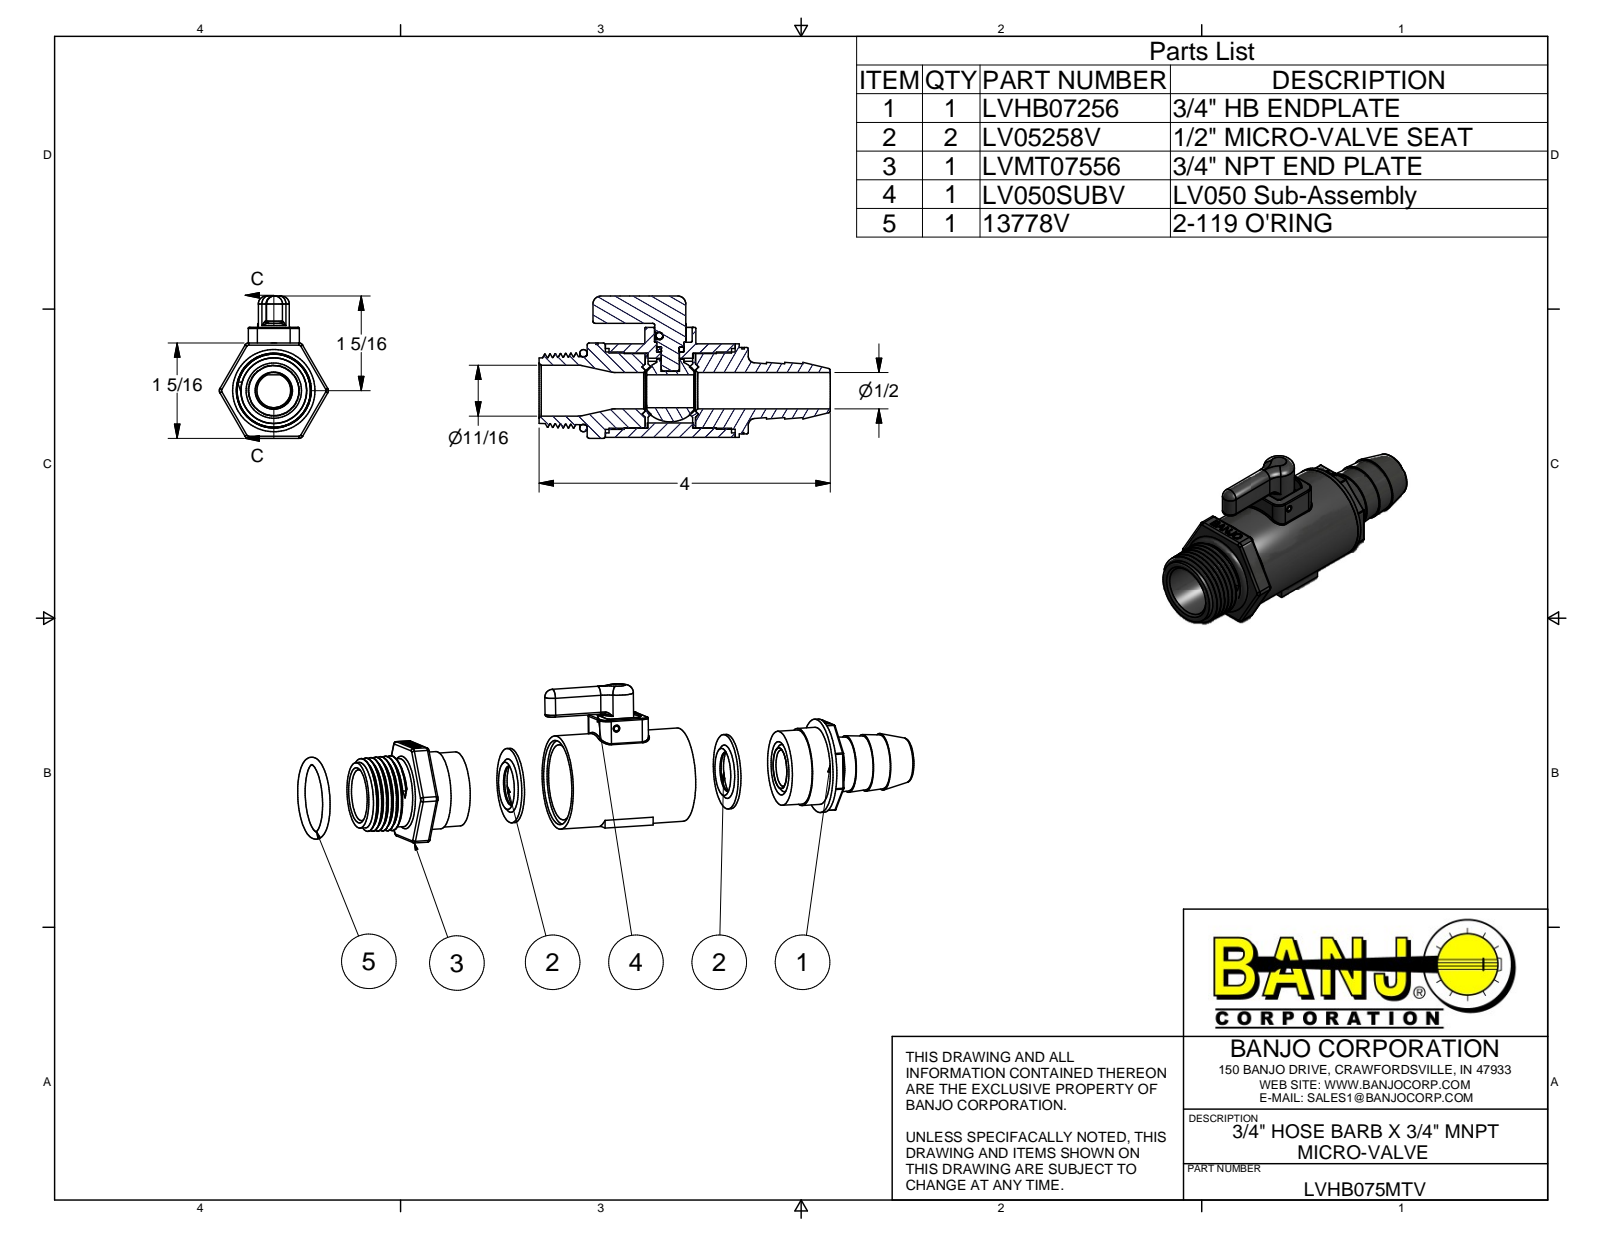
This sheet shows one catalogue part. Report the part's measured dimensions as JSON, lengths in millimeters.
{"part_name": "LV05254A; LV02153B; AQ010V; WS10002 (+7 more)", "step_written_by": "Autodesk Inventor 2014 (AUTOMOTIVE_DESIGN)", "units": "millimeters", "bodies": {"solids": 10, "faces": 701, "planar": 290, "cylindrical": 133, "other": 278}, "overall_size": [101.52, 49.71, 38.02], "volume_mm3": 51198, "surface_area_mm2": 30132, "round_holes": [[2.36, 1], [6.38, 1], [9.3, 1], [9.55, 1], [11.94, 1], [12.7, 1], [13.74, 1], [17.78, 1], [22.61, 1], [26.26, 1], [29.46, 1]], "round_bosses_or_shafts": [[32.64, 1], [27.03, 1], [26.97, 1], [26.01, 1], [25.91, 1], [10.79, 1], [9.52, 1], [9.45, 1]], "partial_cylinders_radius": [[0.25, 16], [0.51, 16], [0.38, 14], [0.76, 14], [1.52, 6], [3.17, 4], [1.27, 2], [2.77, 2]], "face_to_face_distances": [13.84, 31.42, 17.58, 14.86, 30.4, 1.02, 16.56, 45.26, 6.35, 1.27]}
